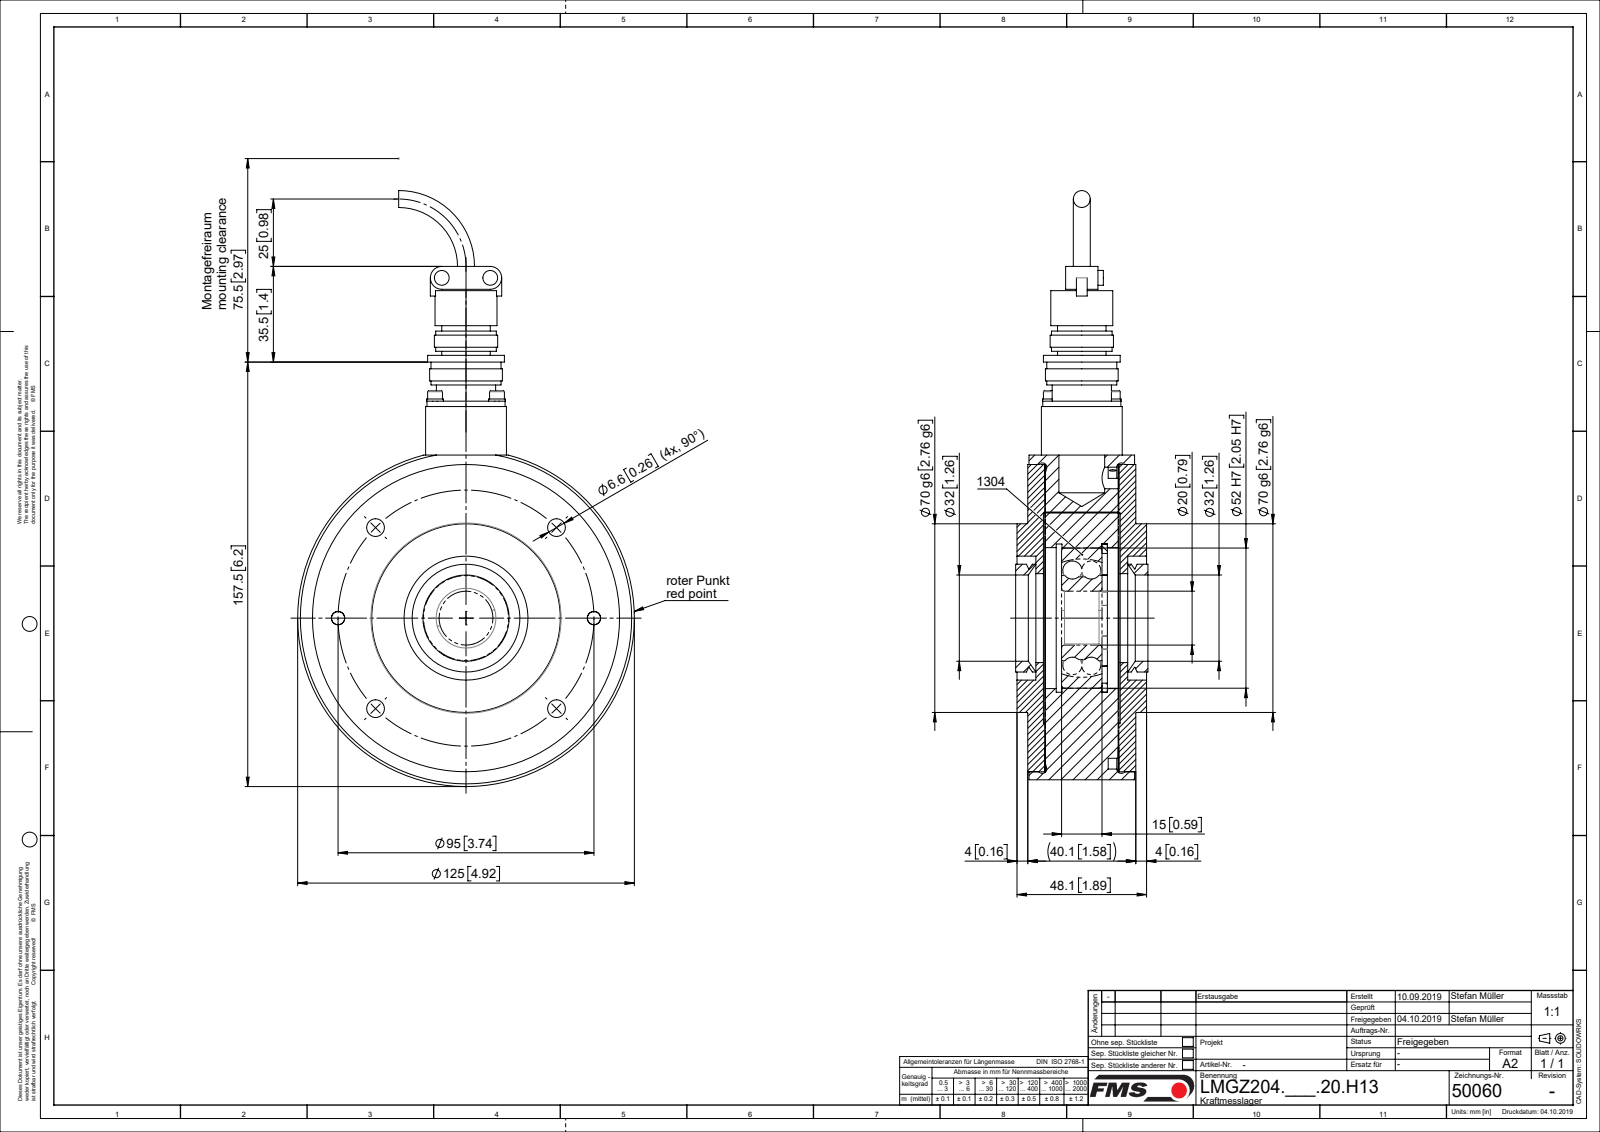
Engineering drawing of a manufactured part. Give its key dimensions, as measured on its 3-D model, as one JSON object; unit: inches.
{"part_name": "ZEICHNUNG7; L50060; L4832404; L48964 (+8 more)", "step_written_by": "Mechanical Desktop 2007 (CONFIG_CONTROL_DESIGN)", "units": "inches", "bodies": {"solids": 21, "faces": 424, "planar": 112, "cylindrical": 252, "other": 60}, "overall_size": [8.707, 4.921, 1.894], "volume_in3": 29.66, "surface_area_in2": 226, "round_holes": [[0.26, 6], [0.102, 4], [0.126, 4], [0.134, 4], [0.197, 2], [0.433, 2], [0.787, 1], [0.906, 1], [1.22, 1], [1.299, 1], [1.492, 1], [1.811, 1]], "round_bosses_or_shafts": [[0.217, 6], [0.244, 4], [0.118, 4], [0.098, 4], [0.394, 2], [0.236, 2], [4.921, 1], [4.488, 1]], "partial_cylinders_radius": [[0.197, 8], [0.167, 2], [1.594, 1], [1.85, 1]], "face_to_face_distances": [1.073, 1.321, 0.248, 0.258, 1.331, 1.063, 1.083, 0.157, 0.415, 1.579], "hole_center_spacings": [1.87, 0.64, 0.906, 1.431, 2.645, 3.456, 1.281, 3.741]}
